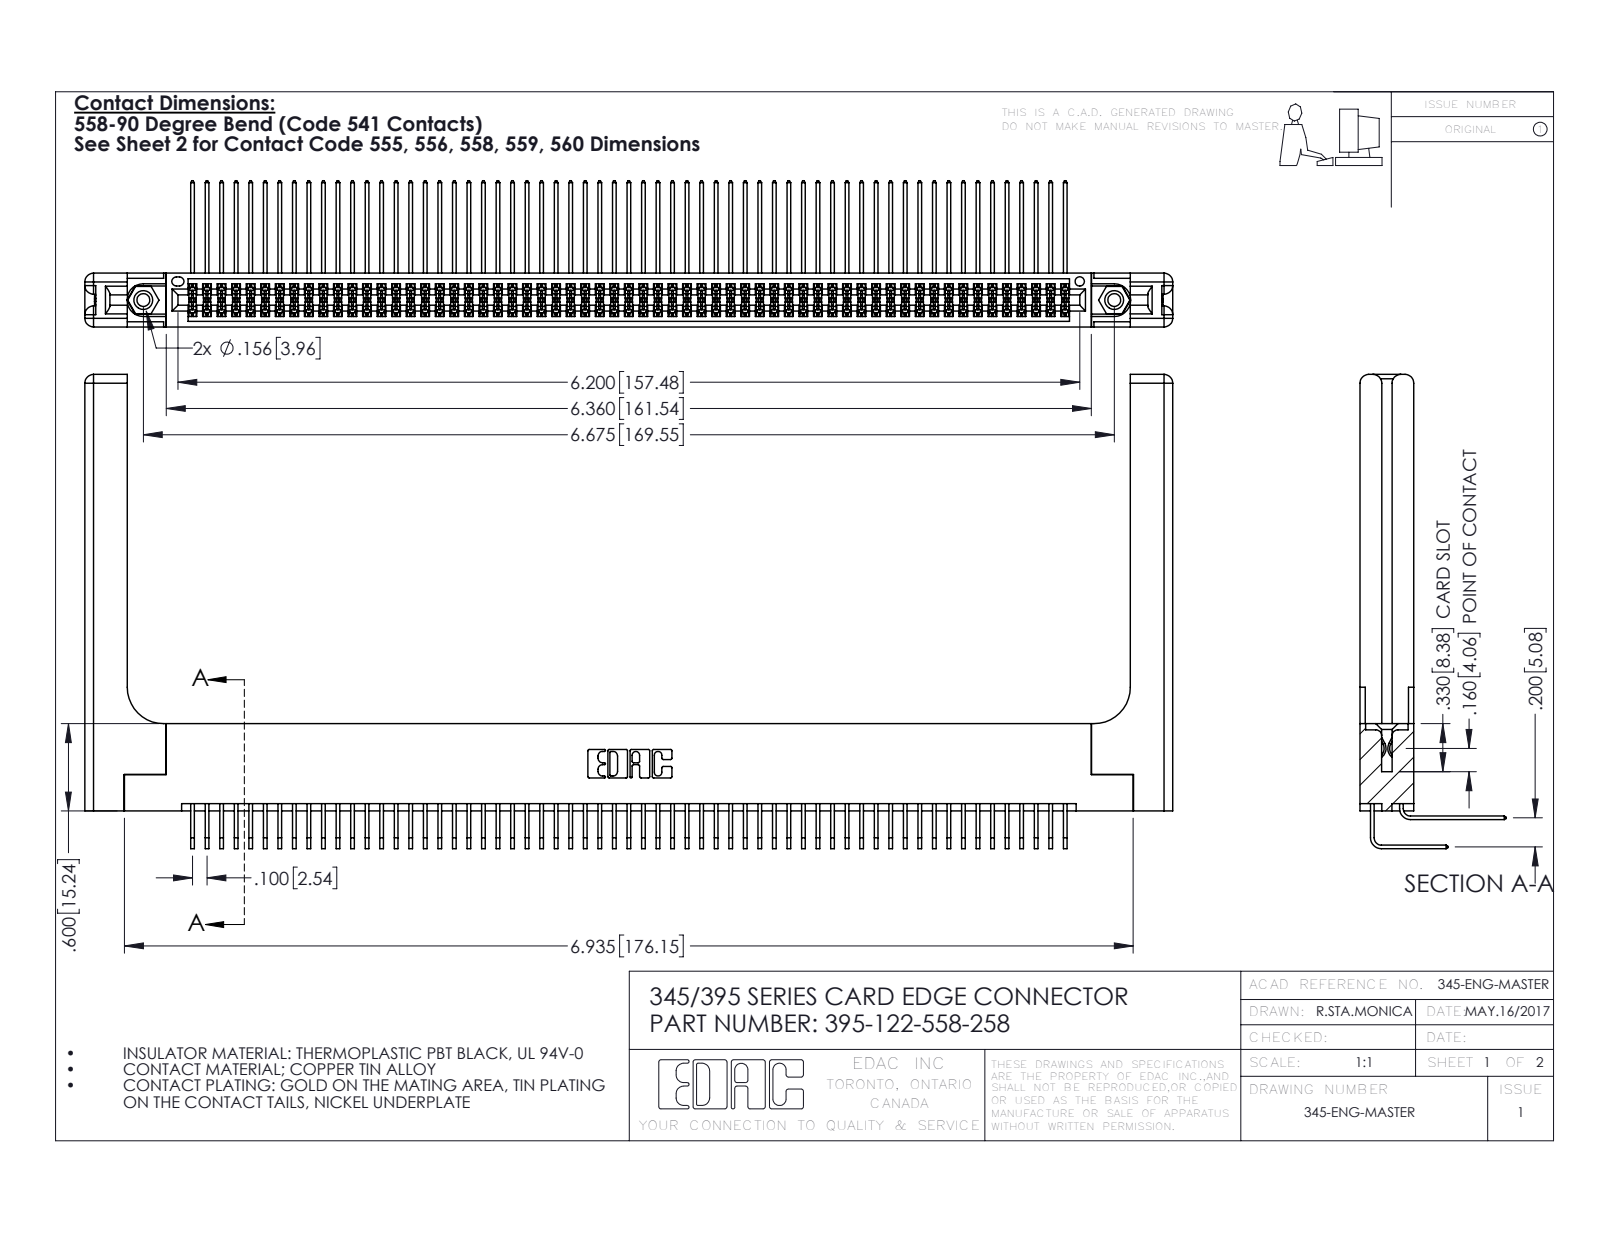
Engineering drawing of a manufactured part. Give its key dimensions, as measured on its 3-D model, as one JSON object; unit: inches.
{"part_name": "395-122-558-258; 345-250-001_345-250-001-102; 345-220-058_345-220-058; 345-292-001_558 Tail - 2 (+2 more)", "step_written_by": "SolidWorks 2016 (CONFIG_CONTROL_DESIGN)", "units": "inches", "bodies": {"solids": 127, "faces": 6726, "planar": 4498, "cylindrical": 2168, "other": 60}, "overall_size": [7.479, 3.259, 1.005], "volume_in3": 1.697, "surface_area_in2": 57.84, "round_holes": [[0.089, 2], [0.125, 2], [0.156, 2], [0.064, 1]], "round_bosses_or_shafts": [[0.155, 2]], "partial_cylinders_radius": [[0.006, 184], [0.01, 22], [0.06, 16], [0.007, 6], [0.031, 6], [0.026, 3], [0.014, 2], [0.019, 2]], "face_to_face_distances": [0.072, 0.298, 0.2, 0.37, 0.098, 0.272, 0.025, 0.225, 0.148, 0.15], "hole_center_spacings": [0.27, 6.439, 6.675]}
